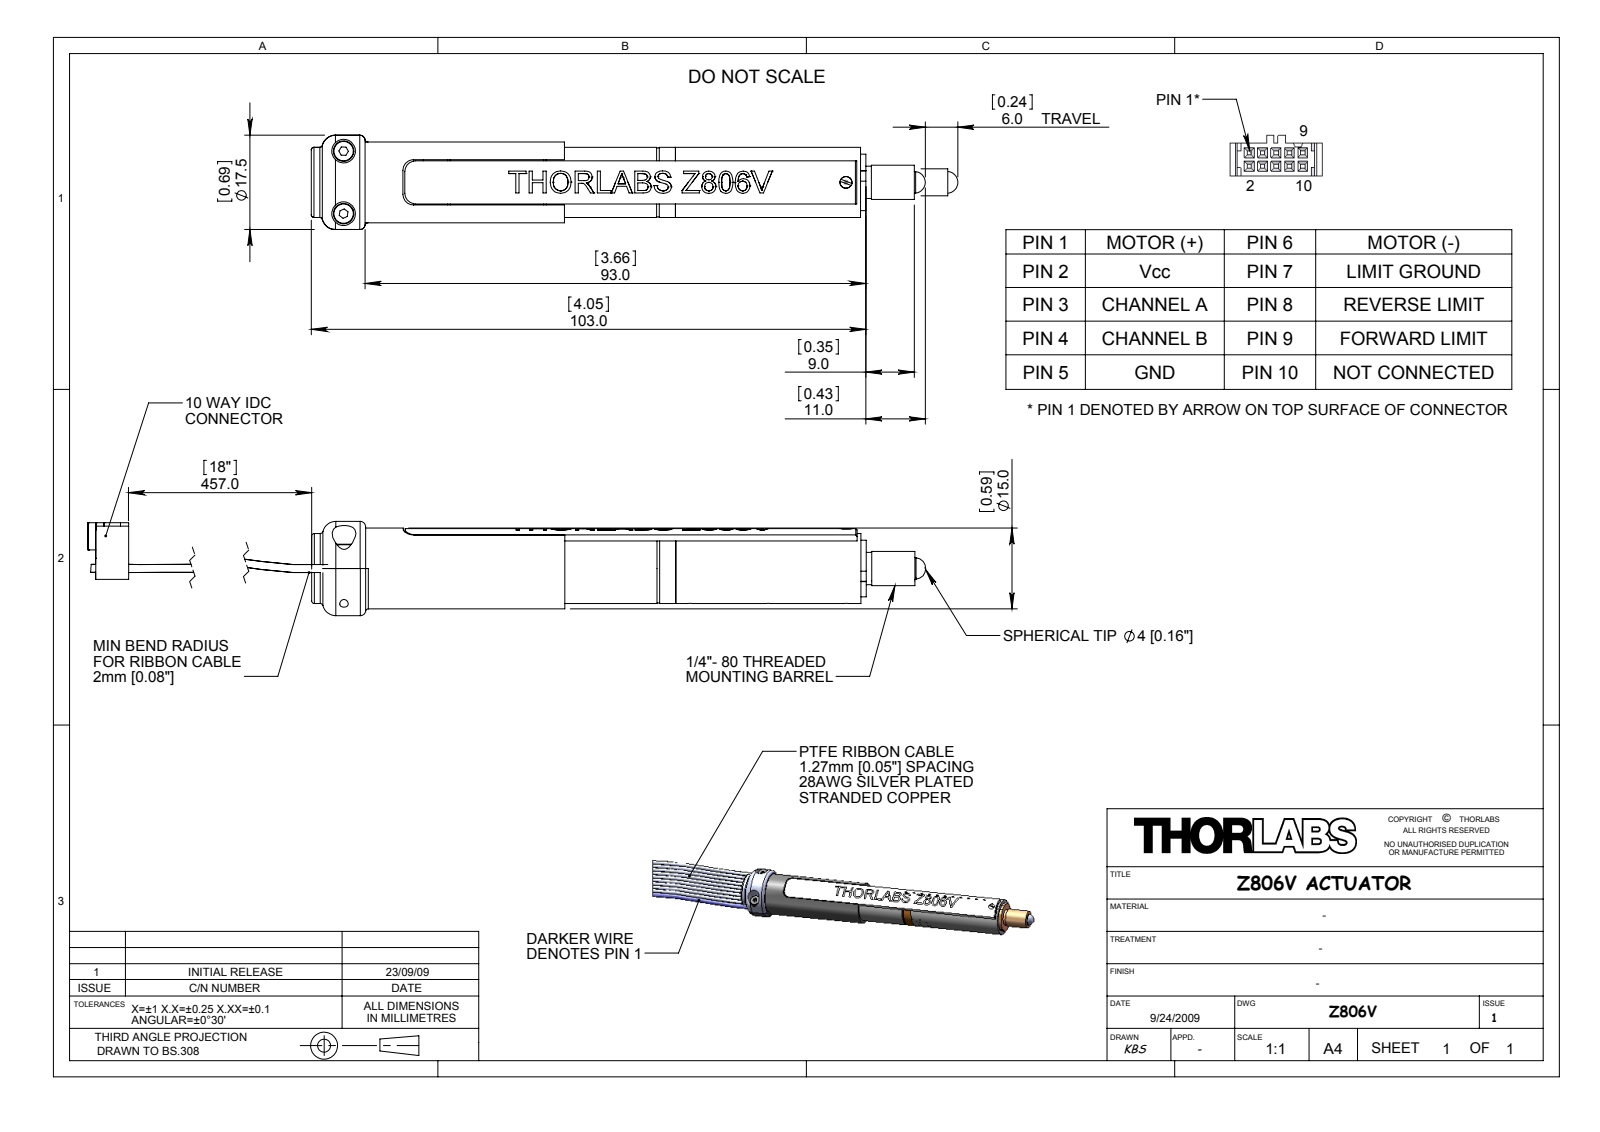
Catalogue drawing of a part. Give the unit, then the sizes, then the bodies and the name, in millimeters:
Units: millimetres
Overall size (bounding box): 113.99 × 17.5 × 17.5
Round holes (diameter × count): ⌀1.6 ×4, ⌀0.95 ×3, ⌀1.2 ×3, ⌀2.1 ×2, ⌀2.2 ×2, ⌀2.7 ×2, ⌀4.4 ×2, ⌀3 ×1, ⌀3.1 ×1, ⌀4.2 ×1, ⌀6.5 ×1, ⌀6.6 ×1
Round bosses / shafts (diameter × count): ⌀3.8 ×2, ⌀2 ×2, ⌀17.5 ×1, ⌀15 ×1, ⌀13 ×1, ⌀12.8 ×1, ⌀12.5 ×1, ⌀12 ×1
Partial cylindrical surfaces — rounded edges, fillets, slot ends (radius × count): R0.17 ×12, R0.5 ×9, R1 ×8, R2 ×8, R1.5 ×2, R5.5 ×1, R6.55 ×1, R7.4 ×1
Main face-to-face distances: 7, 1, 9, 6, 10, 1.2, 6.7, 48.6, 1.5, 57.6
Hole centre spacings: 4.75, 14.5, 64.51, 75.57, 78.96, 89.19, 93.43, 3.4
Volume: 13 666 mm³ · Surface area: 13 492 mm²
Bodies: 12 solids, 634 faces (227 planar, 254 cylindrical, 153 other)
Part name (STEP PRODUCT): Z806v
STEP written by: SolidWorks 2009 (AUTOMOTIVE_DESIGN)
